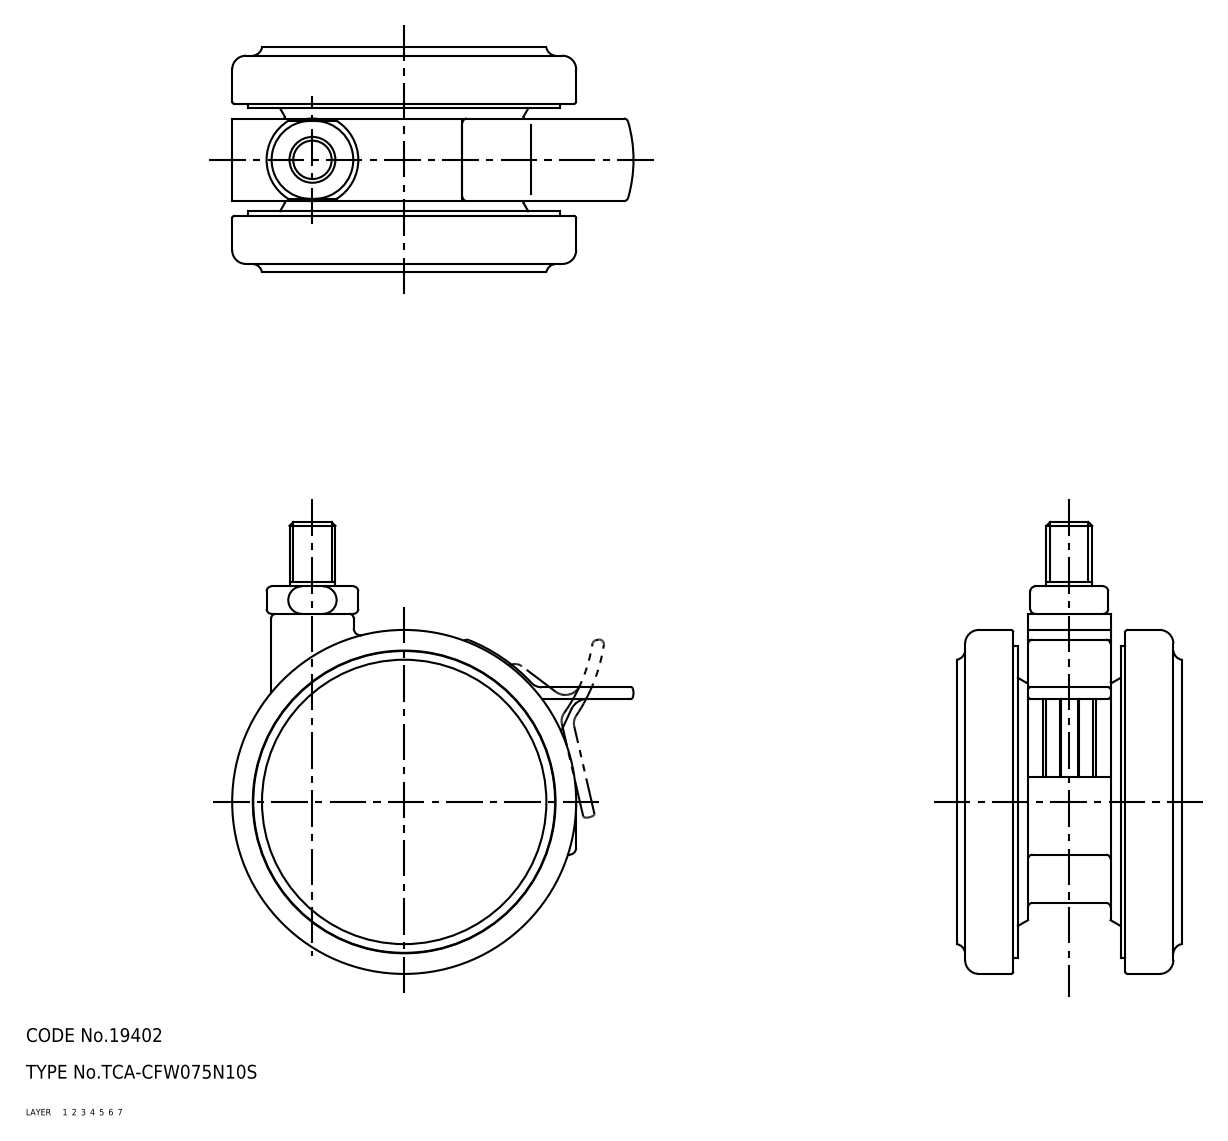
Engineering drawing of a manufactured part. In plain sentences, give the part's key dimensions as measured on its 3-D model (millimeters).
The part is named "TCA-CFW075N10S; caster". Its 3-D file was written by "SolidWorks 2015 (AUTOMOTIVE_DESIGN)". It is 1 solid with 1455 faces: 446 planar, 693 cylindrical and 316 other. Overall it measures 98.5 by 87.5 by 49 millimeters. Its volume is 128 895 cubic millimeters and its surface area 81 428 square millimeters. Round holes: 1 of diameter 1.8, 1 of diameter 3, 1 of diameter 3.3, 1 of diameter 8.1, 1 of diameter 8.4, 1 of diameter 9, 1 of diameter 9.3, 1 of diameter 10.7, 1 of diameter 12.3, 1 of diameter 18, 1 of diameter 58.41, 1 of diameter 59. Round bosses or shafts: 2 of diameter 8, 1 of diameter 75, 1 of diameter 68, 1 of diameter 65.8, 1 of diameter 62.9, 1 of diameter 58.2, 1 of diameter 51, 1 of diameter 18. Partial cylindrical surfaces (rounded edges, fillets, slot ends): 71 of radius 1, 70 of radius 0.8, 54 of radius 0.5, 24 of radius 0.1, 16 of radius 0.2, 9 of radius 1.5, 6 of radius 0.3, 4 of radius 3. The main face-to-face distances are 1.5, 4.5, 12.3, 35.2, 47.5, 3.3, 45.7, 1.8, 44.2, 33.4. The hole center spacings are 32.49.
